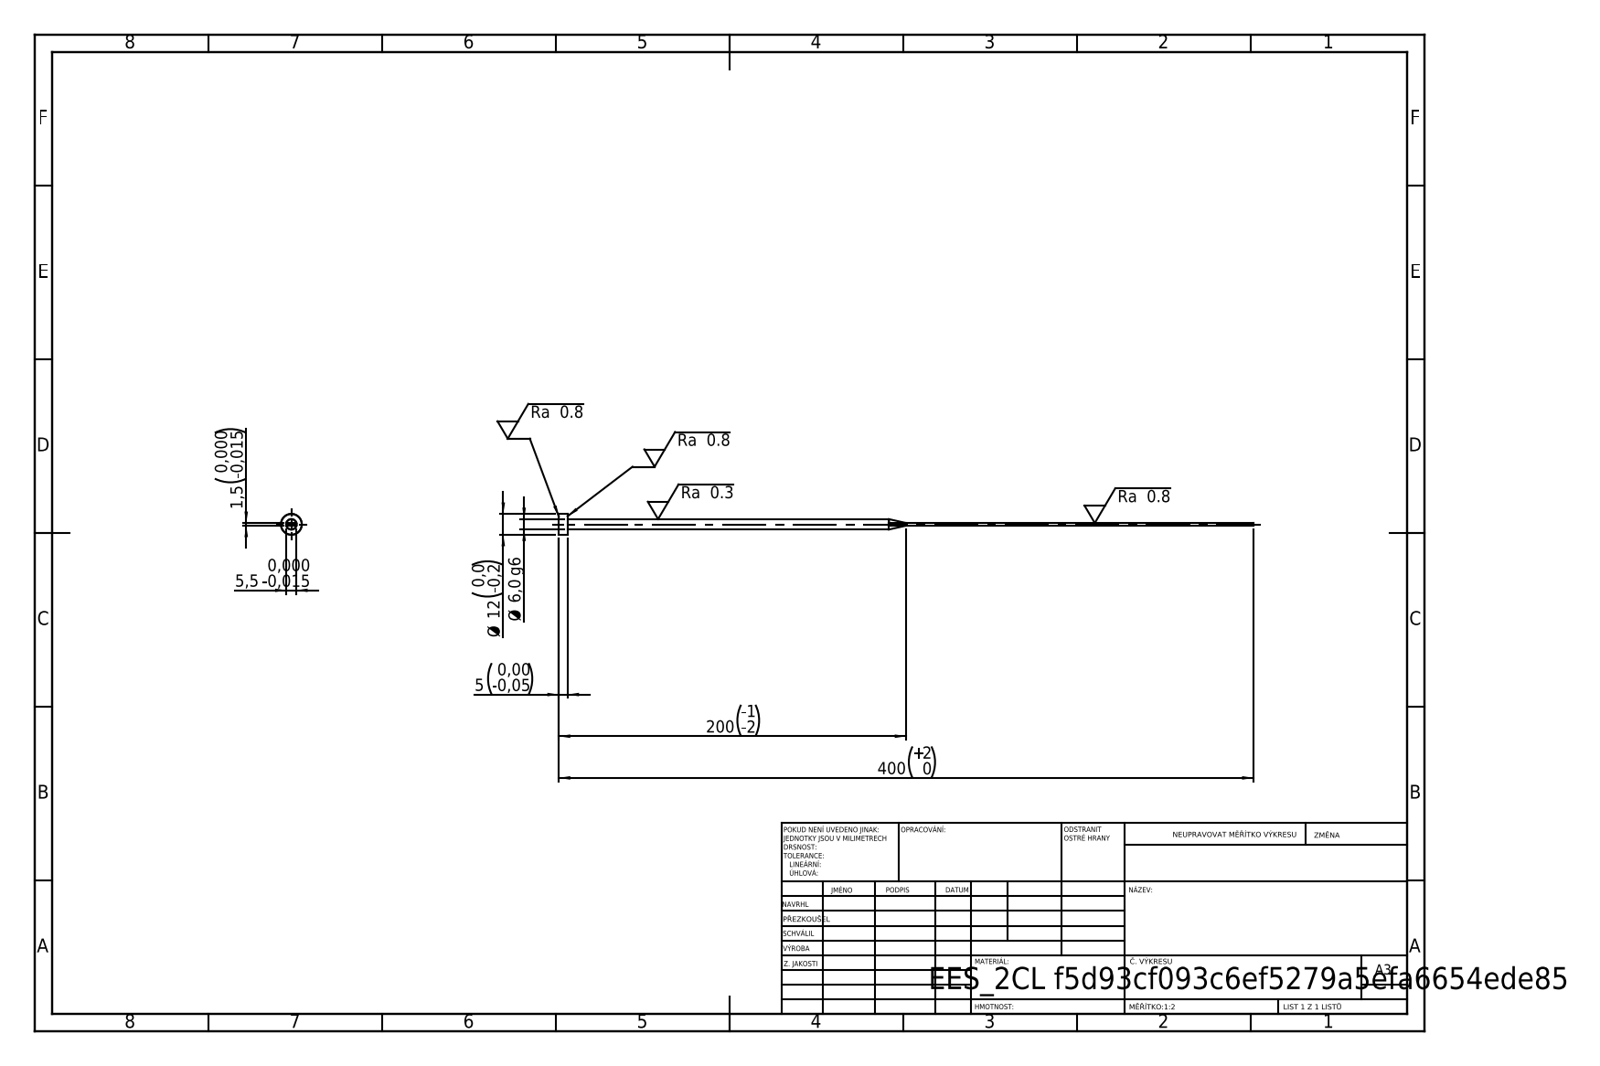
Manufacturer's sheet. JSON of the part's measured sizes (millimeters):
{"step_written_by": "SolidWorks 2019 (CONFIG_CONTROL_DESIGN)", "units": "millimeters", "bodies": {"solids": 1, "faces": 15, "planar": 7, "cylindrical": 4, "other": 4}, "overall_size": [400, 12, 12], "volume_mm3": 7622, "surface_area_mm2": 6841, "round_bosses_or_shafts": [[12, 1], [6, 1]], "face_to_face_distances": [1.5, 5.5, 5, 400, 395]}
